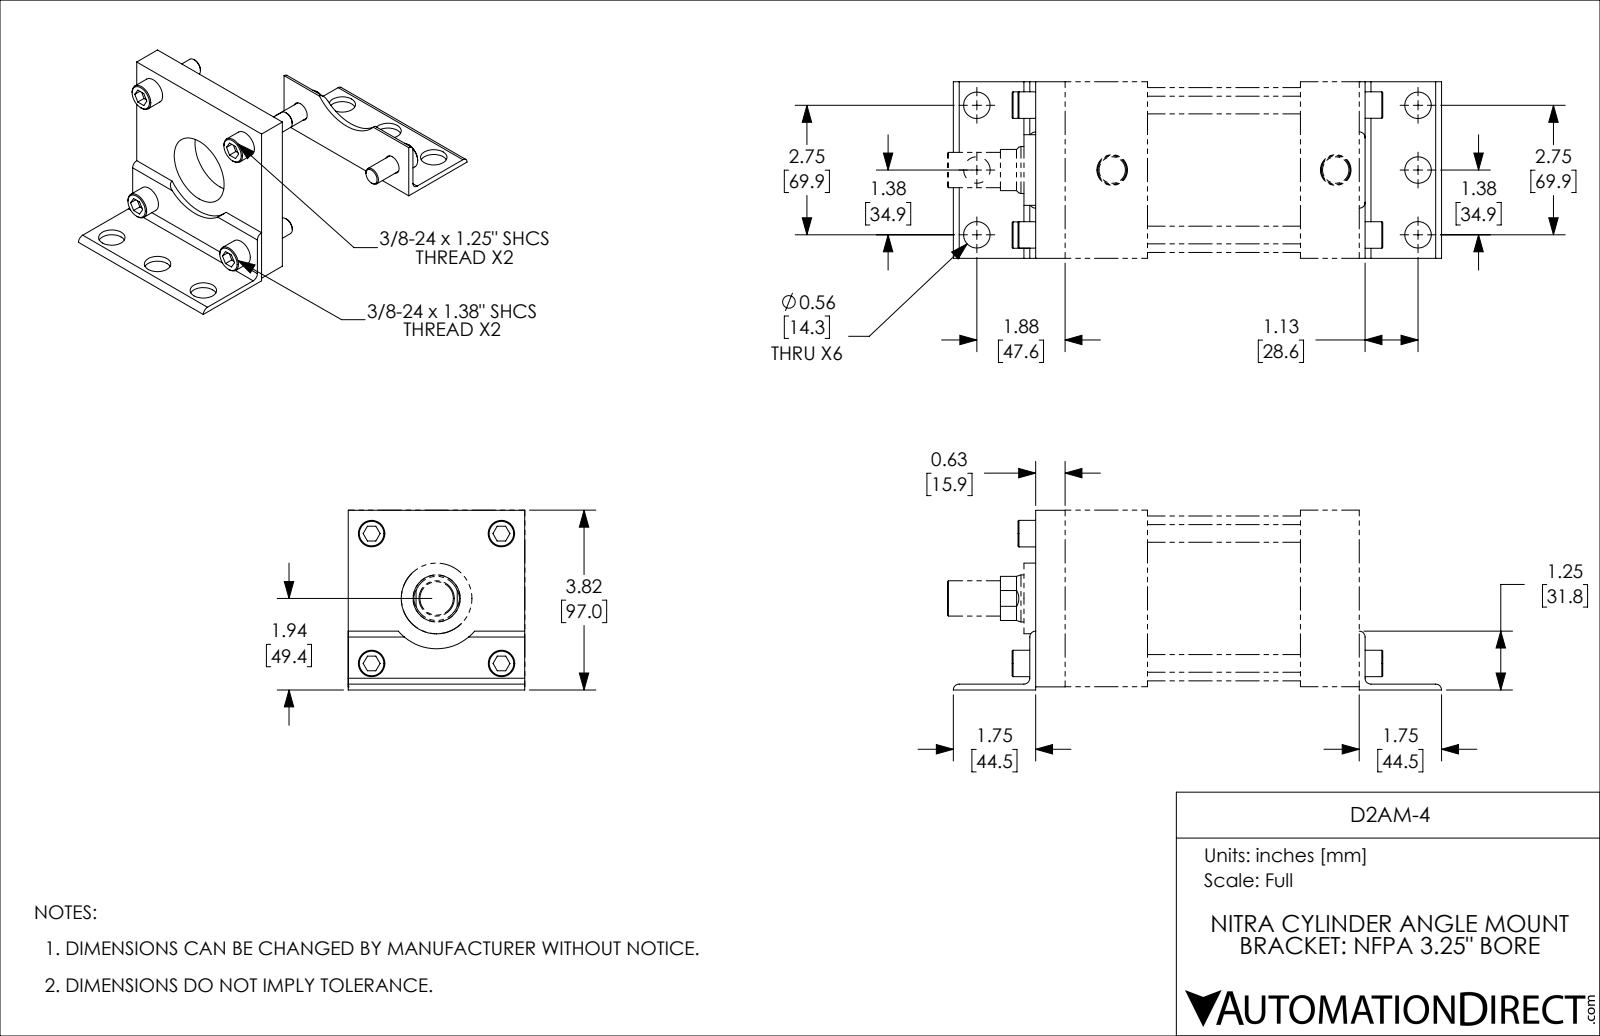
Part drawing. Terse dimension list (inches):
name: D2AM-4_1; D2AM-4; D2AM-4_2
written by: SolidWorks 2019 (CONFIG_CONTROL_DESIGN)
unit: in
bodies: 9 solids, 166 faces (78 planar, 64 cylindrical, 24 other)
size: 7.925 × 3.817 × 3.75
volume: 10.89 in³; area: 96.66 in²
holes: 7× ⌀0.406, 6× ⌀0.563, 1× ⌀1.5
bosses: 6× ⌀0.562, 3× ⌀0.375, 3× ⌀0.375
rounds: 6× R0.125, 1× R1.062
face distances: 0.625, 0.125, 0.125, 4.55, 3.75, 3.8, 4.426, 4.425, 0.625, 3.925
hole spacings: 2.758, 1.95, 7.06, 6.925, 1.375, 1.375, 2.75, 2.757
